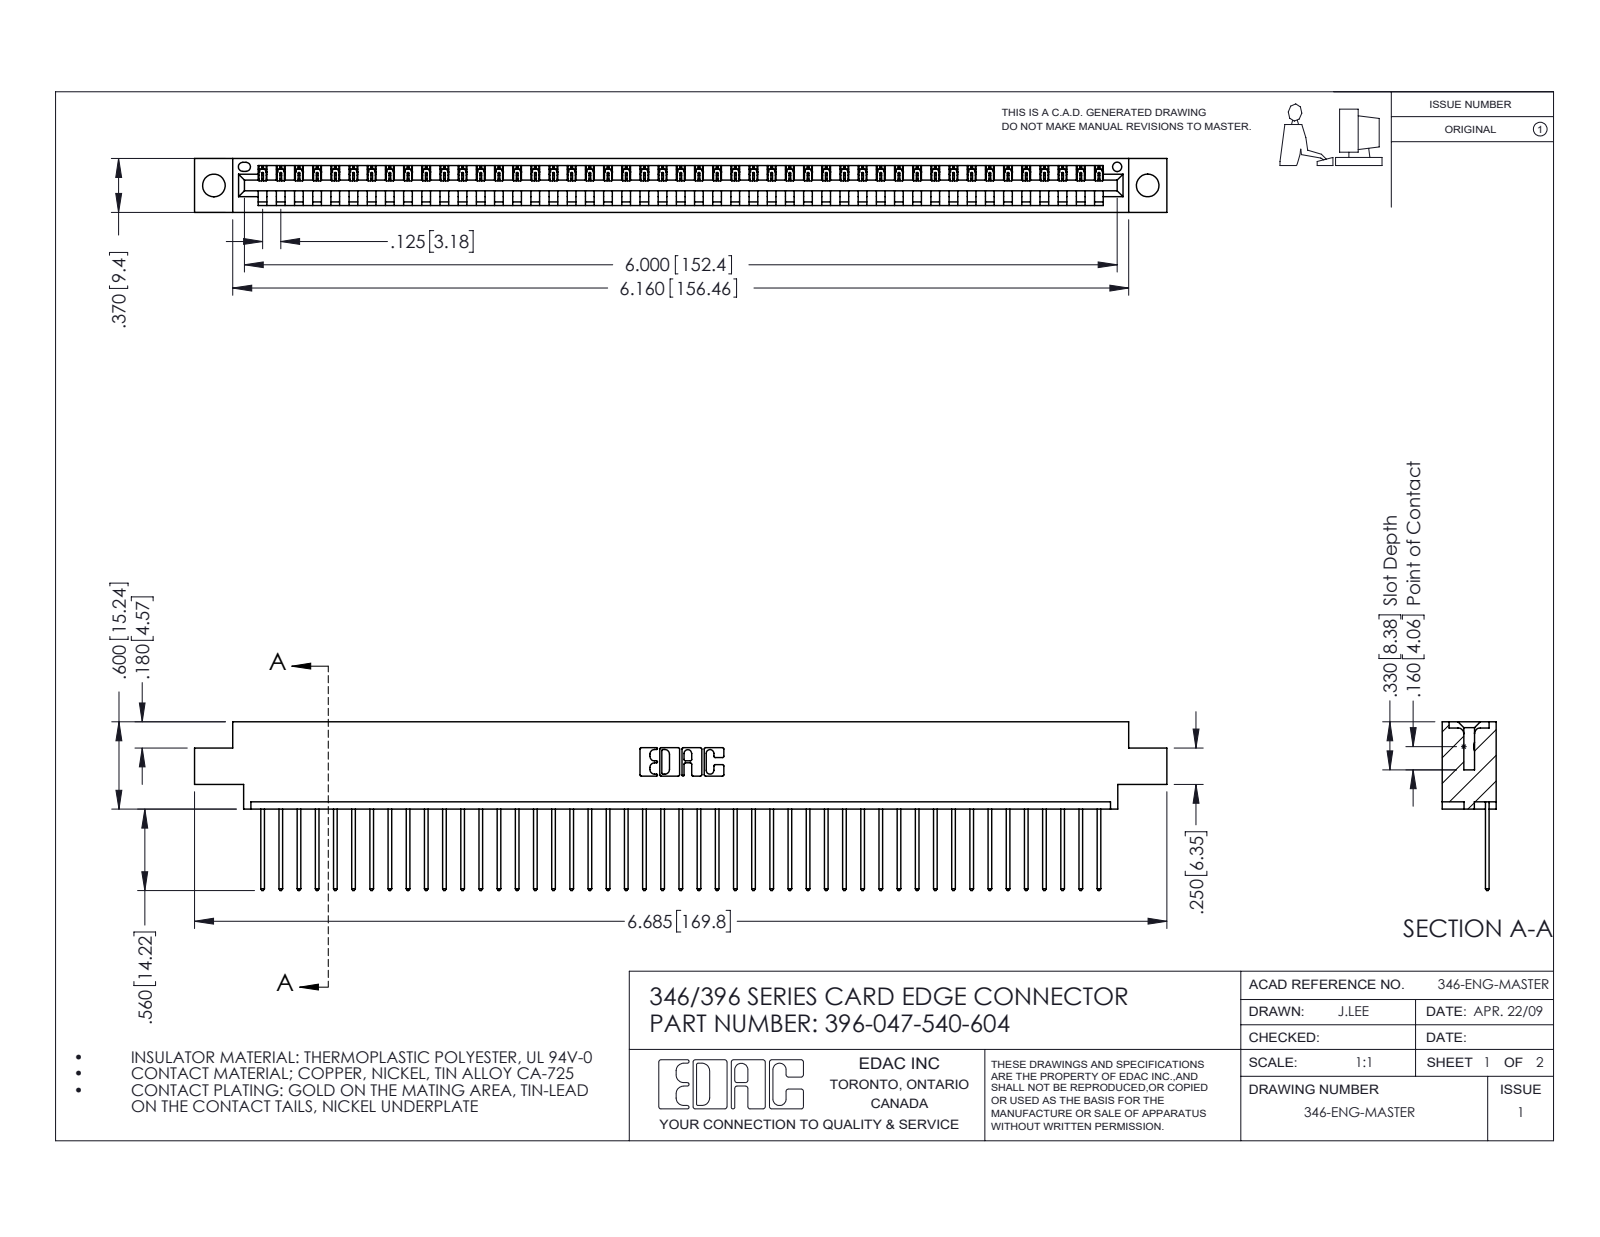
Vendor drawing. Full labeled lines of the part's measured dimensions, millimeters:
Part name (STEP PRODUCT): 396-047-540-604; 345-292-001_345-293-140; 346 Part_0.170 Offset - 0.156 Dia-TH
STEP written by: SolidWorks 2016 (CONFIG_CONTROL_DESIGN)
Units: millimetres
Bodies: 48 solids, 2852 faces (1960 planar, 892 cylindrical, 0 other)
Overall size (bounding box): 169.8 × 29.5 × 9.4
Volume: 16 100 mm³ · Surface area: 20 620 mm²
Round holes (diameter × count): ⌀4 ×2, ⌀1.6 ×1
Partial cylindrical surfaces — rounded edges, fillets, slot ends (radius × count): R0.2 ×94, R0.3 ×94, R0.3 ×22, R0.2 ×6, R0.8 ×6, R0.7 ×3, R0.8 ×2, R1 ×2
Main face-to-face distances: 1.2, 8.2, 9.4, 6.4, 1.8, 7.6, 0.6, 3.8, 5.6, 2.5
Hole centre spacings: 6.2, 157.8, 163.1
